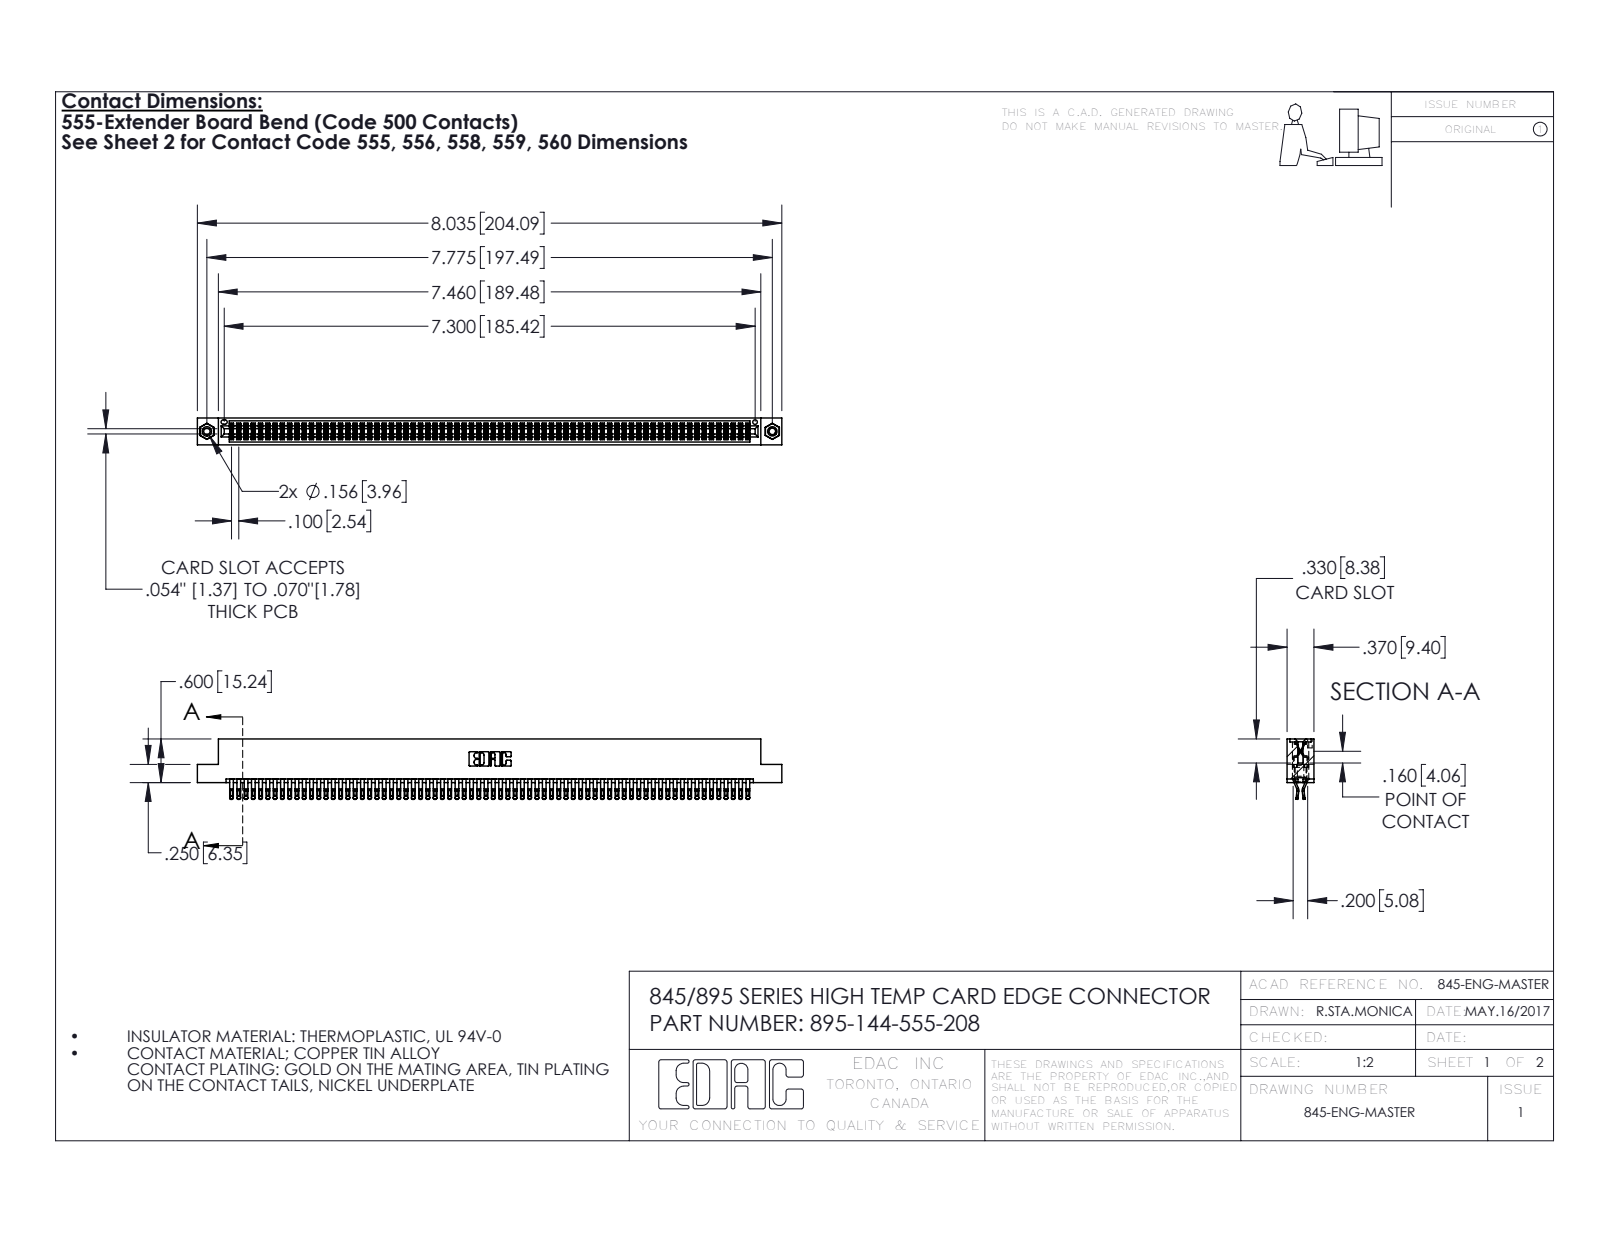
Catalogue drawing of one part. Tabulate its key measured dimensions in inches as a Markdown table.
| quantity | value |
| --- | --- |
| part name | 345-292-001_555 Tail; 345-250-001_345-250-003-102; 395-144-555-208; 345 Part_Flush Mounting Lugs - 0.156 Dia-TI |
| STEP written by | SolidWorks 2016 (CONFIG_CONTROL_DESIGN) |
| units | inches |
| bodies | 147 solids, 8250 faces (4576 planar, 3658 cylindrical, 16 other) |
| overall size | 8.035 × 0.832 × 0.37 |
| volume | 1.252 in³ |
| surface area | 50.18 in² |
| round holes (diameter × count) | 0.089 × 2, 0.125 × 2, 0.156 × 2, 0.064 × 1 |
| round bosses / shafts (diameter × count) | 0.155 × 2 |
| partial cylindrical surfaces (radius × count) | 0.016 × 360, 0.02 × 288, 0.006 × 216, 0.01 × 22, 0.007 × 6, 0.031 × 6, 0.026 × 3, 0.01 × 2 |
| main face-to-face distances | 0.072, 0.298, 0.025, 0.37, 0.2, 0.098, 0.272, 0.225, 0.175, 0.149 |
| hole center spacings | 0.27, 7.539, 7.775 |
